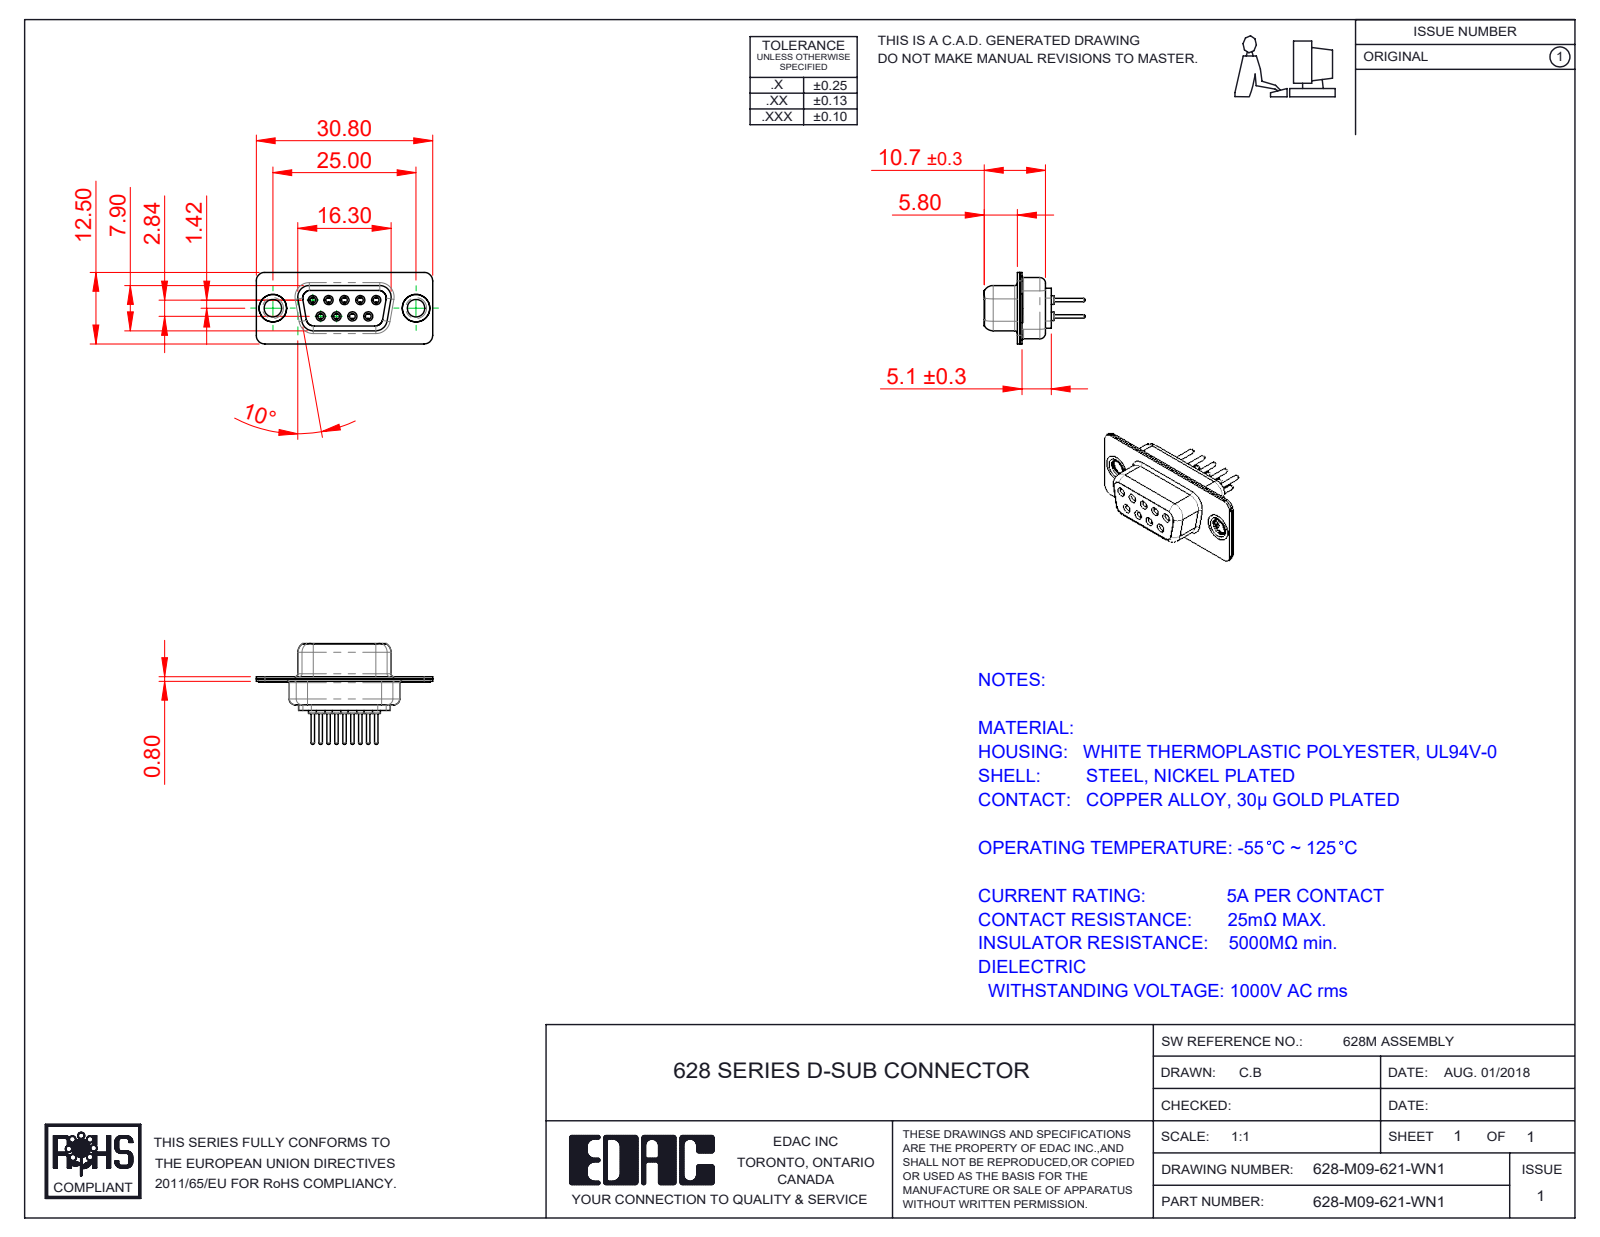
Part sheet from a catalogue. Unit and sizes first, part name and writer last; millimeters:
Units: millimetres
Overall size (bounding box): 30.8 × 17.6 × 12.5
Round holes (diameter × count): ⌀1 ×9, ⌀1.1 ×9, ⌀1.7 ×9, ⌀1.8 ×9, ⌀2 ×9, ⌀3.05 ×2, ⌀4 ×2, ⌀4.8 ×2
Round bosses / shafts (diameter × count): ⌀2.2 ×9, ⌀1.6 ×9, ⌀1.5 ×9, ⌀0.6 ×9, ⌀5 ×2, ⌀4.9 ×2, ⌀3.55 ×2
Partial cylindrical surfaces — rounded edges, fillets, slot ends (radius × count): R1.5 ×16, R2 ×12, R1.35 ×8, R1.6 ×8, R0.25 ×4, R0.5 ×4, R0.6 ×4, R0.65 ×4
Main face-to-face distances: 0.4, 1.4, 0.45, 8.45, 0.8, 8.9, 1.8, 1, 6.2, 1.35
Hole centre spacings: 3.16, 2.77, 5.54, 5.03, 5.04, 8.31, 7.1, 7.48
Volume: 1 624 mm³ · Surface area: 4 277 mm²
Bodies: 14 solids, 748 faces (202 planar, 292 cylindrical, 254 other)
Part name (STEP PRODUCT): 628M Shell Front_09 Contacts; 628M Contact Row 2_21; 628M Shell Rear_09 Contacts; 628M Housing_09 Contacts (+3 more)
STEP written by: SolidWorks 2020 (CONFIG_CONTROL_DESIGN)
